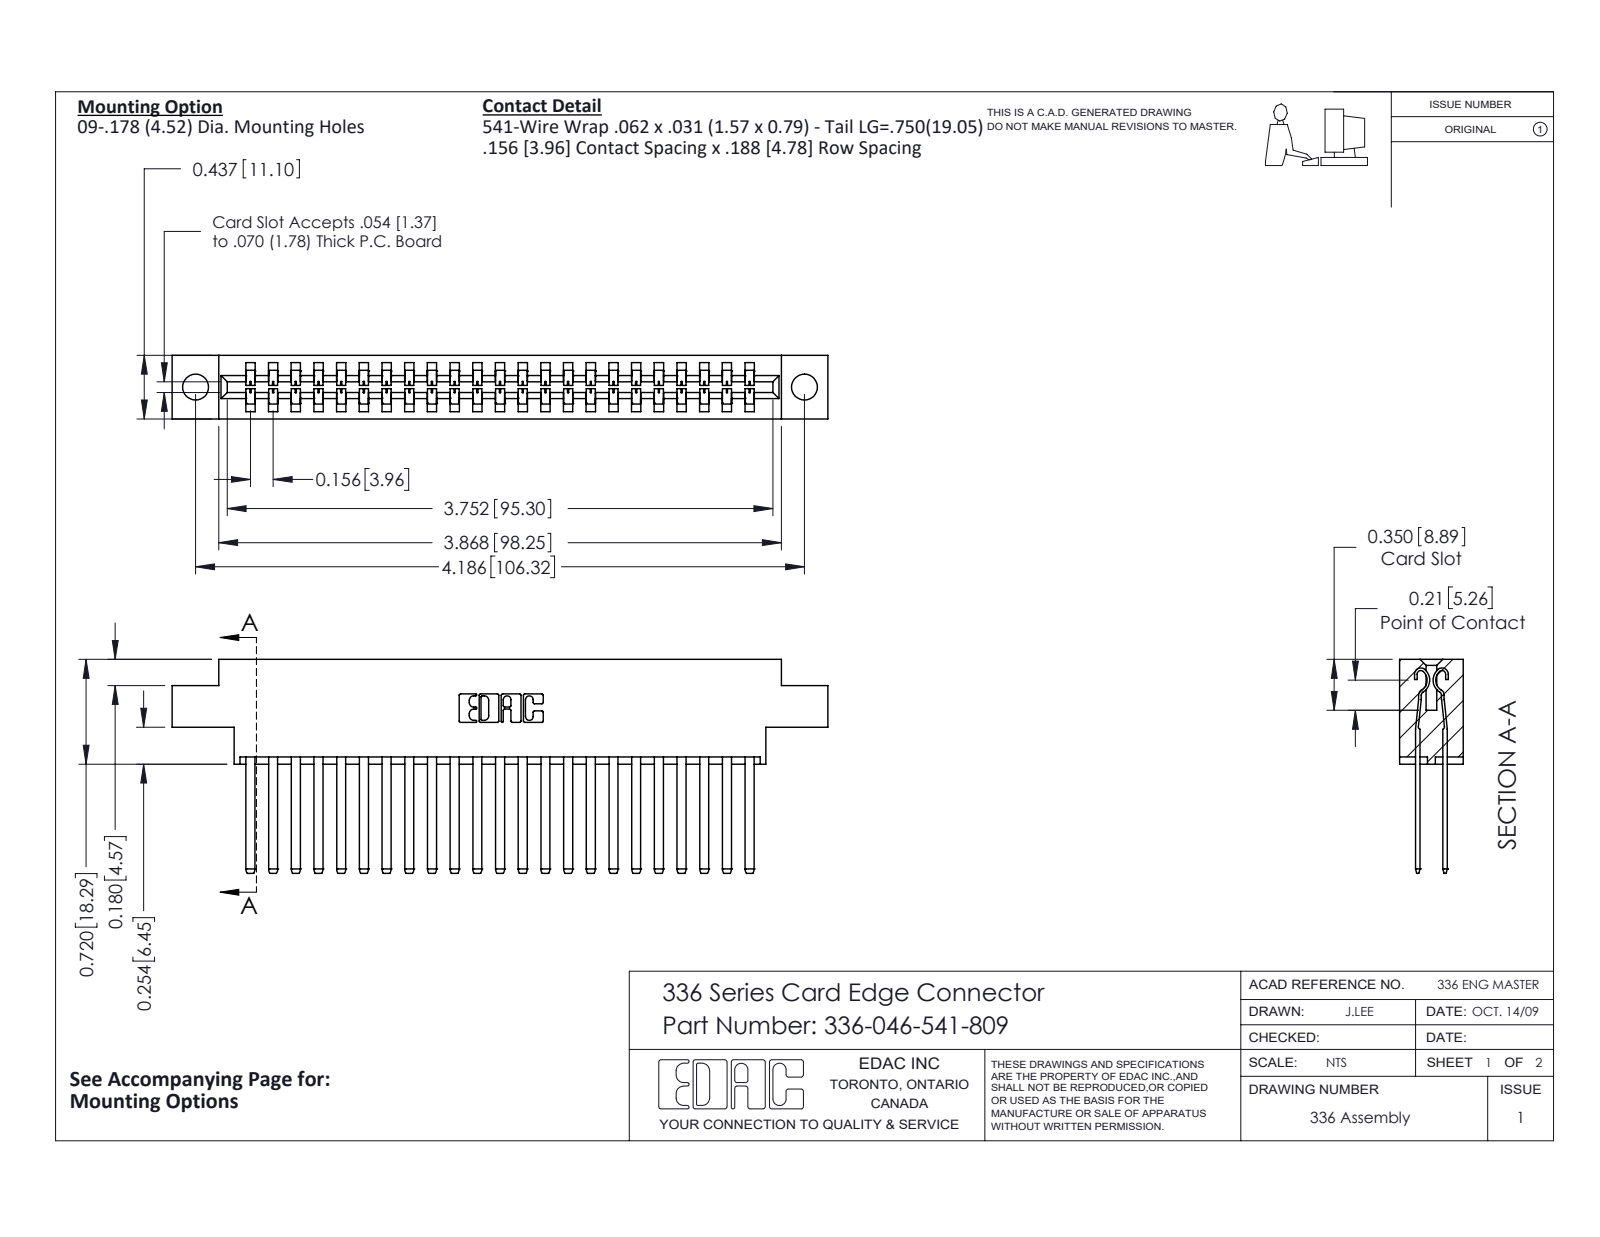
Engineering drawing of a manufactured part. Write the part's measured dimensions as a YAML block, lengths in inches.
part_name: "336 Part_Offset - .178 Dia - TH; 336-046-541-809; 336-290-001_336-290-541"
step_written_by: "SolidWorks 2020 (CONFIG_CONTROL_DESIGN)"
units: inches
bodies: {solids: 47, faces: 2050, planar: 1270, cylindrical: 780, other: 0}
overall_size: [4.509, 1.47, 0.437]
volume: 1.033
surface_area: 32.92
round_holes:
  - {diameter: 0.178, count: 2}
partial_cylinders:
  - {radius: 0.004, count: 92}
  - {radius: 0.056, count: 46}
  - {radius: 0.01, count: 22}
  - {radius: 0.007, count: 6}
  - {radius: 0.031, count: 6}
  - {radius: 0.022, count: 4}
  - {radius: 0.04, count: 4}
  - {radius: 0.026, count: 3}
face_to_face_distances: [0.188, 0.328, 0.14, 0.297, 0.109, 0.031, 0.437, 0.033, 0.156, 0.181]
hole_center_spacings: [4.186]
